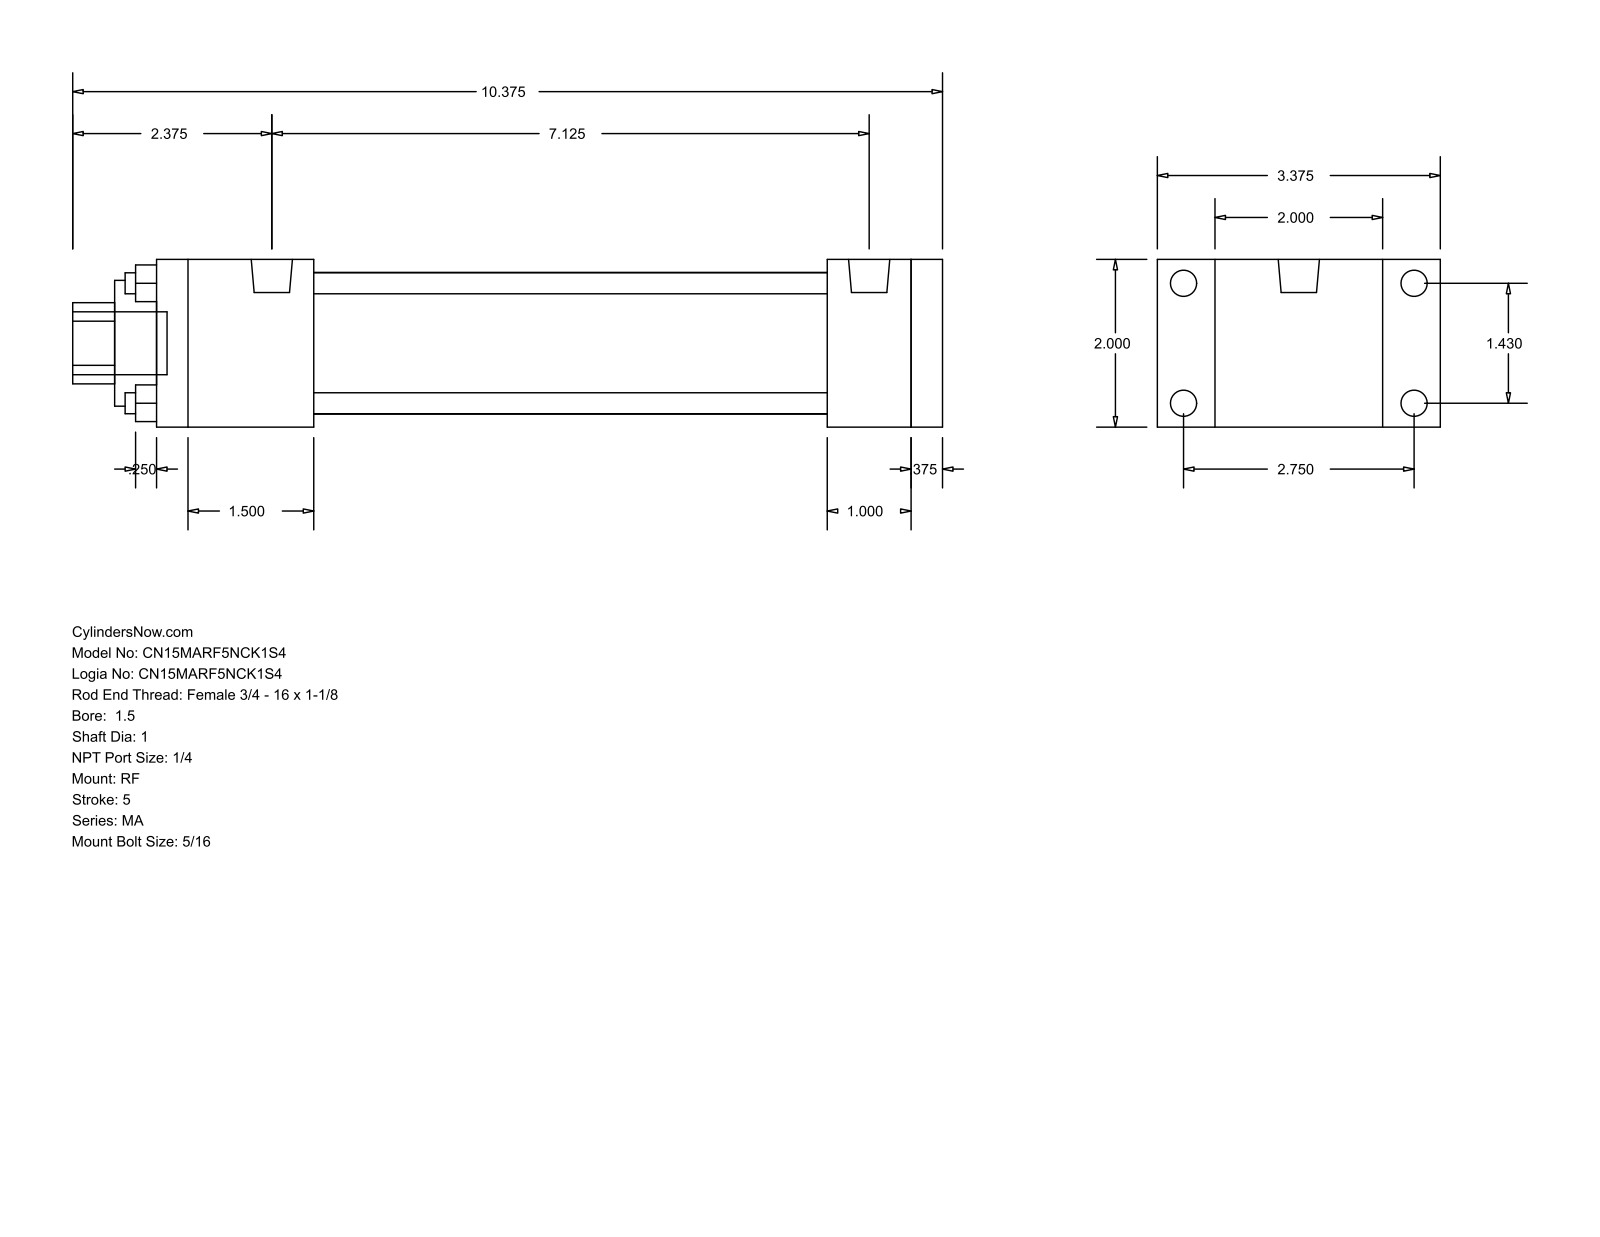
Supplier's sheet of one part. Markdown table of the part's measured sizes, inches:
| quantity | value |
| --- | --- |
| part name | MA_RF__0150_1 |
| STEP written by | GSSL Pune (CONFIG_CONTROL_DESIGN) |
| units | inches |
| bodies | 0 solids, 92 faces (64 planar, 28 cylindrical, 0 other) |
| overall size | 10.375 × 3.375 × 2 |
| round holes (diameter × count) | 0.25 × 4, 1 × 1, 1.5 × 1, 1.69 × 1 |
| round bosses / shafts (diameter × count) | 0.313 × 8, 0.492 × 2, 0.75 × 1 |
| partial cylindrical surfaces (radius × count) | 0.484 × 1 |
| main face-to-face distances | 2, 0.375, 9.375, 9, 1, 8, 1.375, 1.875, 6.125, 7.125 |
| hole center spacings | 1.011, 1.43, 2.022 |
